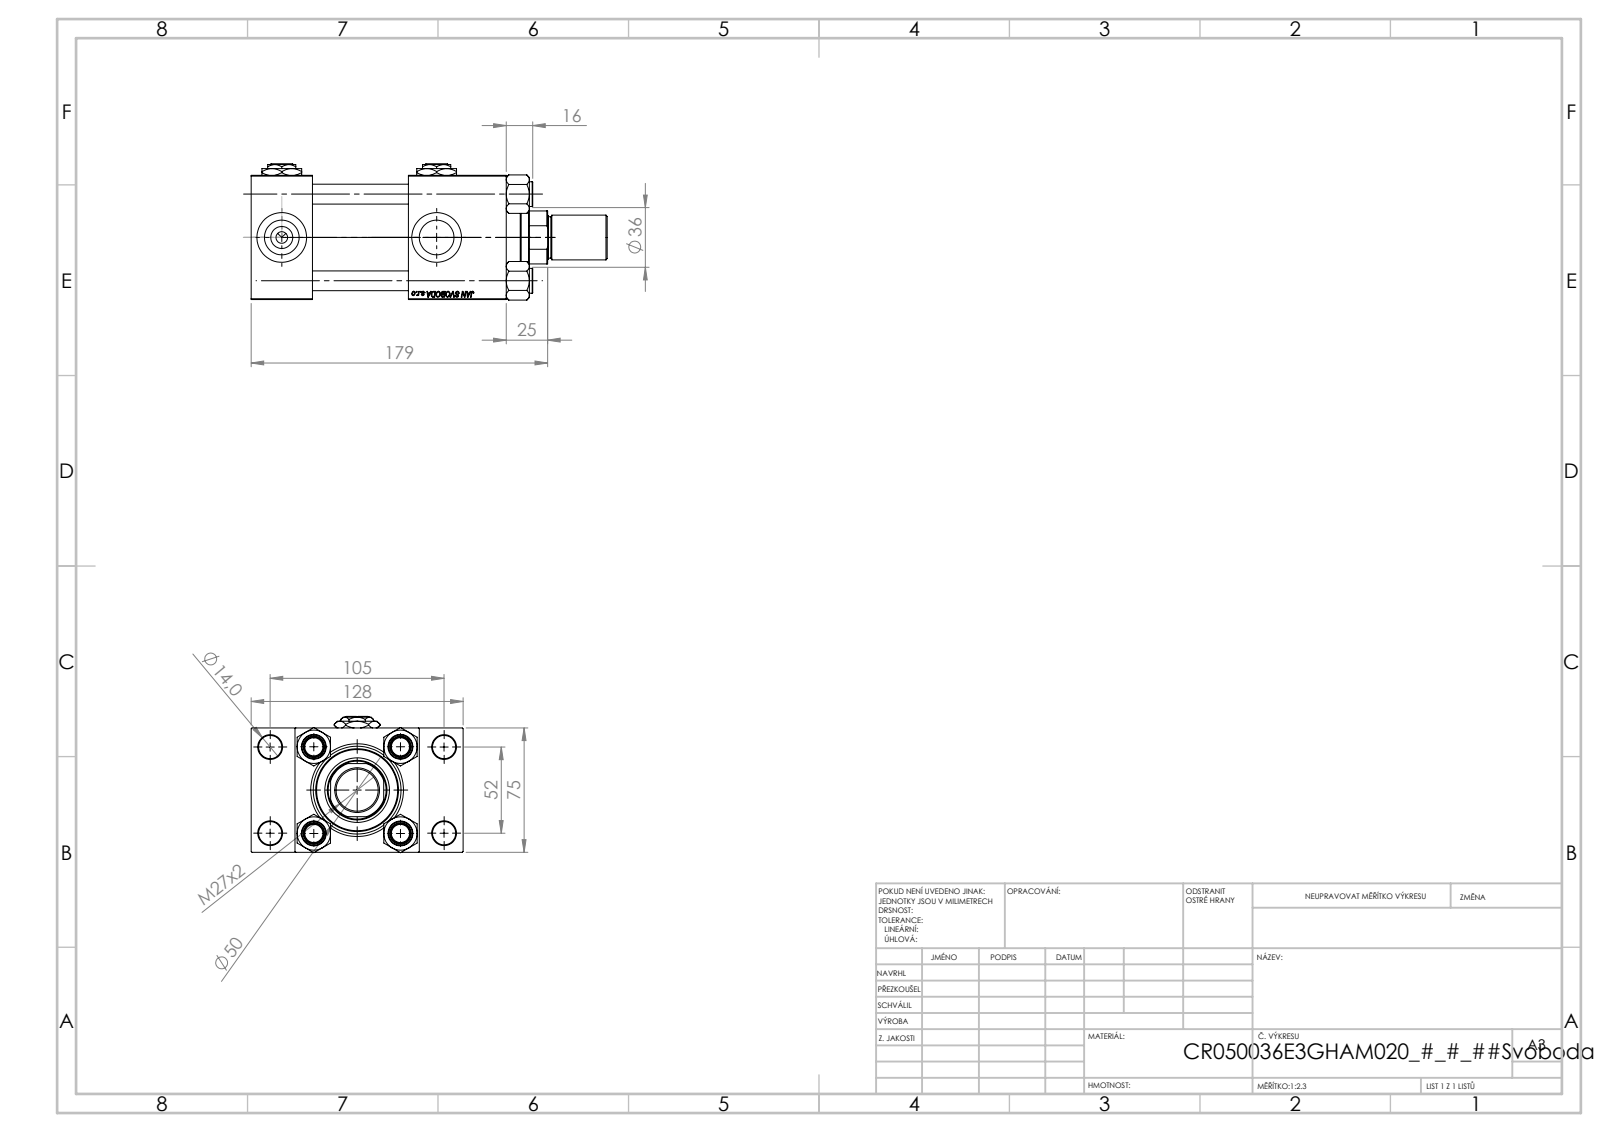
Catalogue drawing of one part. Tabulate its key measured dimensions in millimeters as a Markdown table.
| quantity | value |
| --- | --- |
| part name | Zatka_pro_OIL_PORT; V215_VC_A; NUT_M5_E; V215CR_TYCINKA_E (+3 more) |
| STEP written by | SolidWorks 2019 (CONFIG_CONTROL_DESIGN) |
| units | millimeters |
| bodies | 14 solids, 1250 faces (549 planar, 101 cylindrical, 600 other) |
| overall size | 215 × 128 × 82.27 |
| volume | 832 218 mm³ |
| surface area | 190 104 mm² |
| round holes (diameter × count) | 12 × 4, 14 × 4, 20.96 × 4, 30 × 4, 7 × 3, 25.5 × 1, 36 × 1, 39 × 1, 41 × 1, 53 × 1 |
| round bosses / shafts (diameter × count) | 15 × 4, 56 × 1, 50 × 1, 27 × 1, 25 × 1 |
| partial cylindrical surfaces (radius × count) | 17.5 × 1 |
| main face-to-face distances | 75, 37, 26.5, 101.5, 95, 117, 154, 59, 58, 125.3 |
| hole center spacings | 26.35, 36.98, 52.3, 58.43, 58.59, 78.65, 94.37, 52 |
